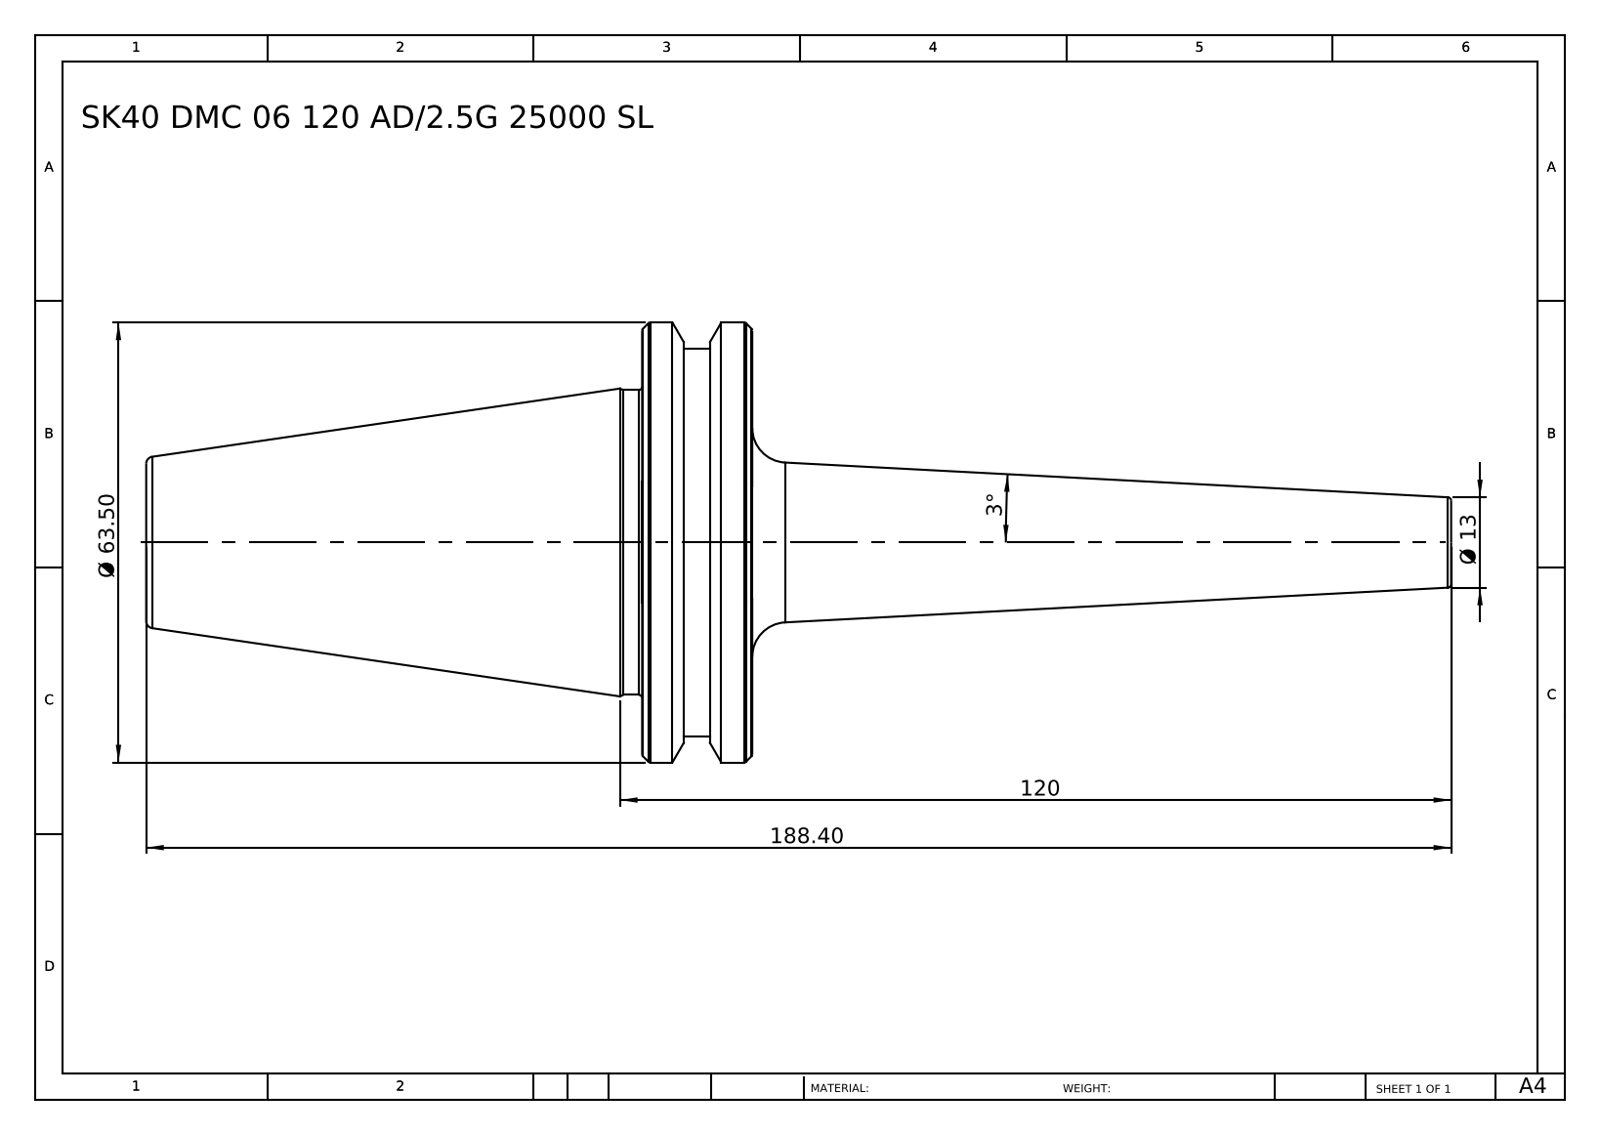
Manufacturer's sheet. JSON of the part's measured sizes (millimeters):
{"part_name": "SK 40 DMC 06 120 AD-2.5G 25000 SL", "step_written_by": "SolidWorks 2014 (CONFIG_CONTROL_DESIGN)", "units": "millimeters", "bodies": {"solids": 1, "faces": 64, "planar": 6, "cylindrical": 8, "other": 50}, "overall_size": [188.4, 63.5, 63.5], "volume_mm3": 144723, "surface_area_mm2": 22290, "round_bosses_or_shafts": [[63.5, 1], [56, 1], [44, 1]], "face_to_face_distances": [15.9, 87.5, 71.6, 6.1, 9.8, 81.4, 9.9, 3.8, 6, 77.6]}
